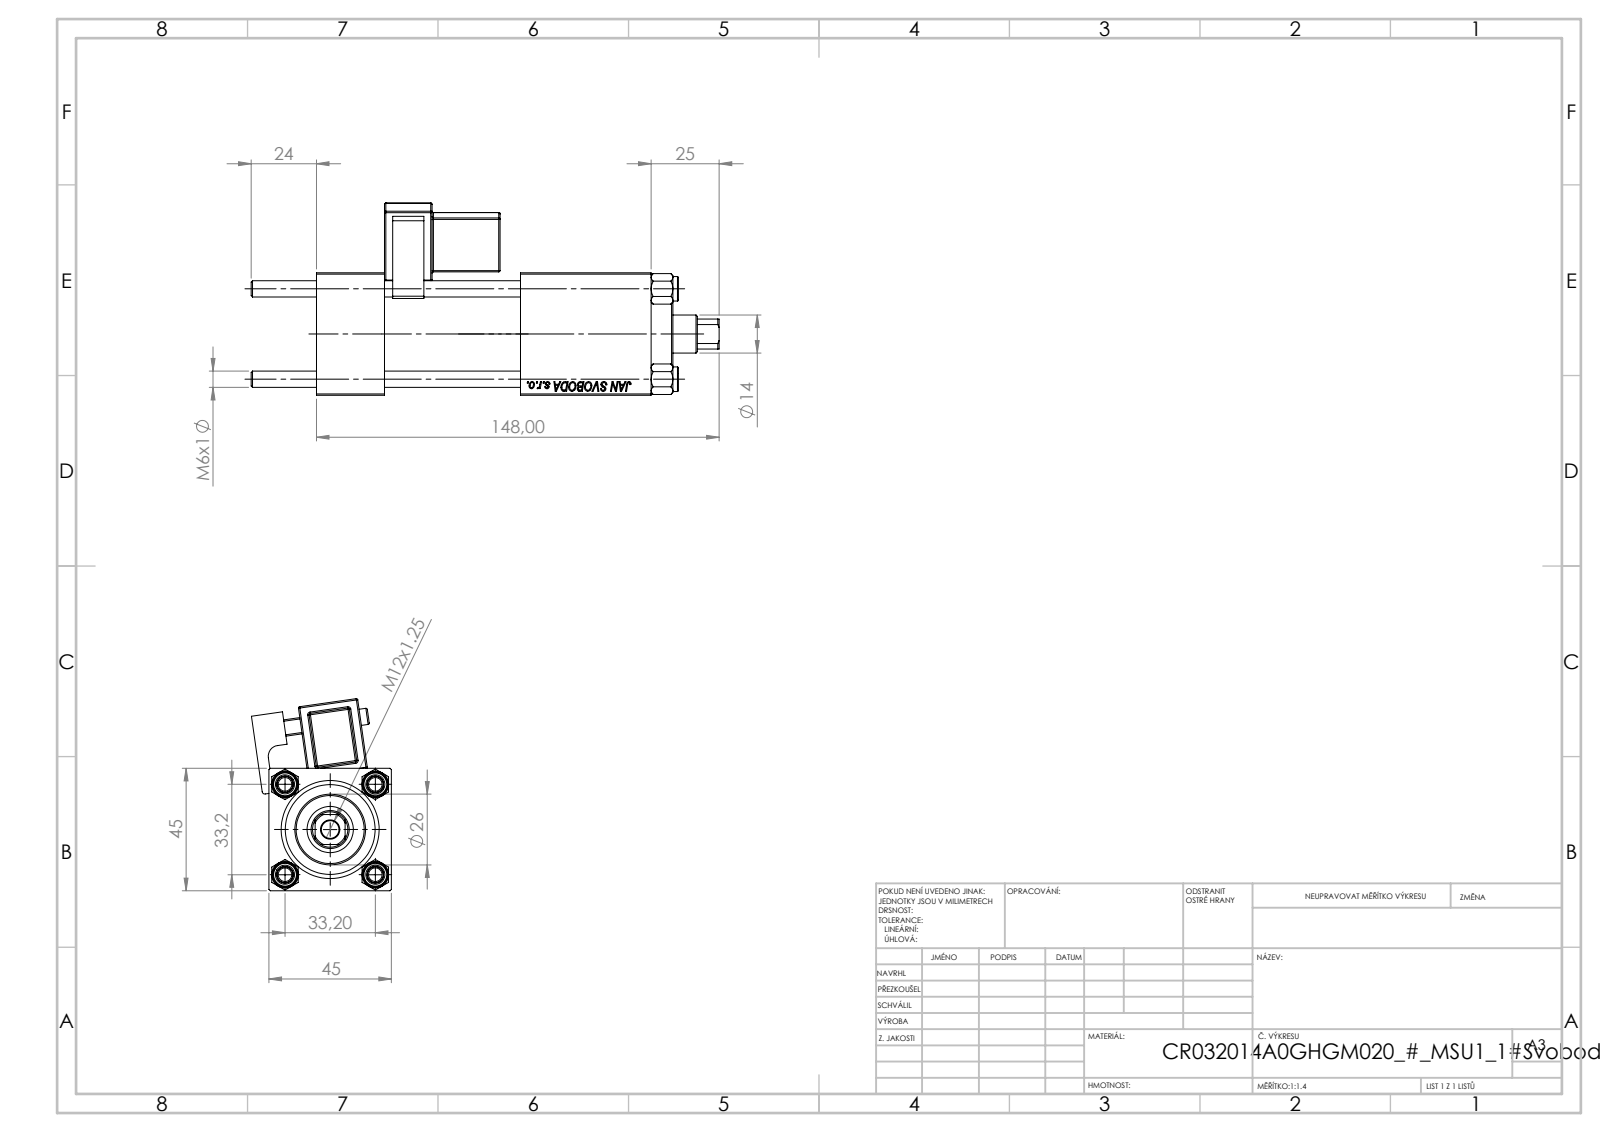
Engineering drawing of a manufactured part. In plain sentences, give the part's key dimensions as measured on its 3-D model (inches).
The part is named "NUT_M5; V215CR_BODY_A; V215CR_VCP; V215CR_MSU (+2 more)". Its 3-D file was written by "SolidWorks 2019 (CONFIG_CONTROL_DESIGN)". It is 12 solids with 1212 faces: 550 planar, 108 cylindrical and 554 other. Overall it measures 6.772 by 2.779 by 2.024 inches. Its volume is 13.34 cubic inches and its surface area 122.2 square inches. Round holes: 4 of diameter 0.236, 2 of diameter 0.276, 2 of diameter 0.518, 2 of diameter 0.787, 1 of diameter 0.256, 1 of diameter 0.551, 1 of diameter 0.669, 1 of diameter 0.945, 1 of diameter 1.26, 1 of diameter 1.299. Round bosses or shafts: 4 of diameter 0.354, 1 of diameter 1.496, 1 of diameter 1.024, 1 of diameter 0.236. Partial cylindrical surfaces (rounded edges, fillets, slot ends): 24 of radius 0.02, 1 of radius 0.039, 1 of radius 0.098, 1 of radius 0.157, 1 of radius 0.256. The main face-to-face distances are 1.772, 0.984, 4.843, 3.858, 1.969, 2.953, 1.89, 3.713, 2.728, 0.76. The hole center spacings are 0.924, 1.307, 1.848, 2.972.
